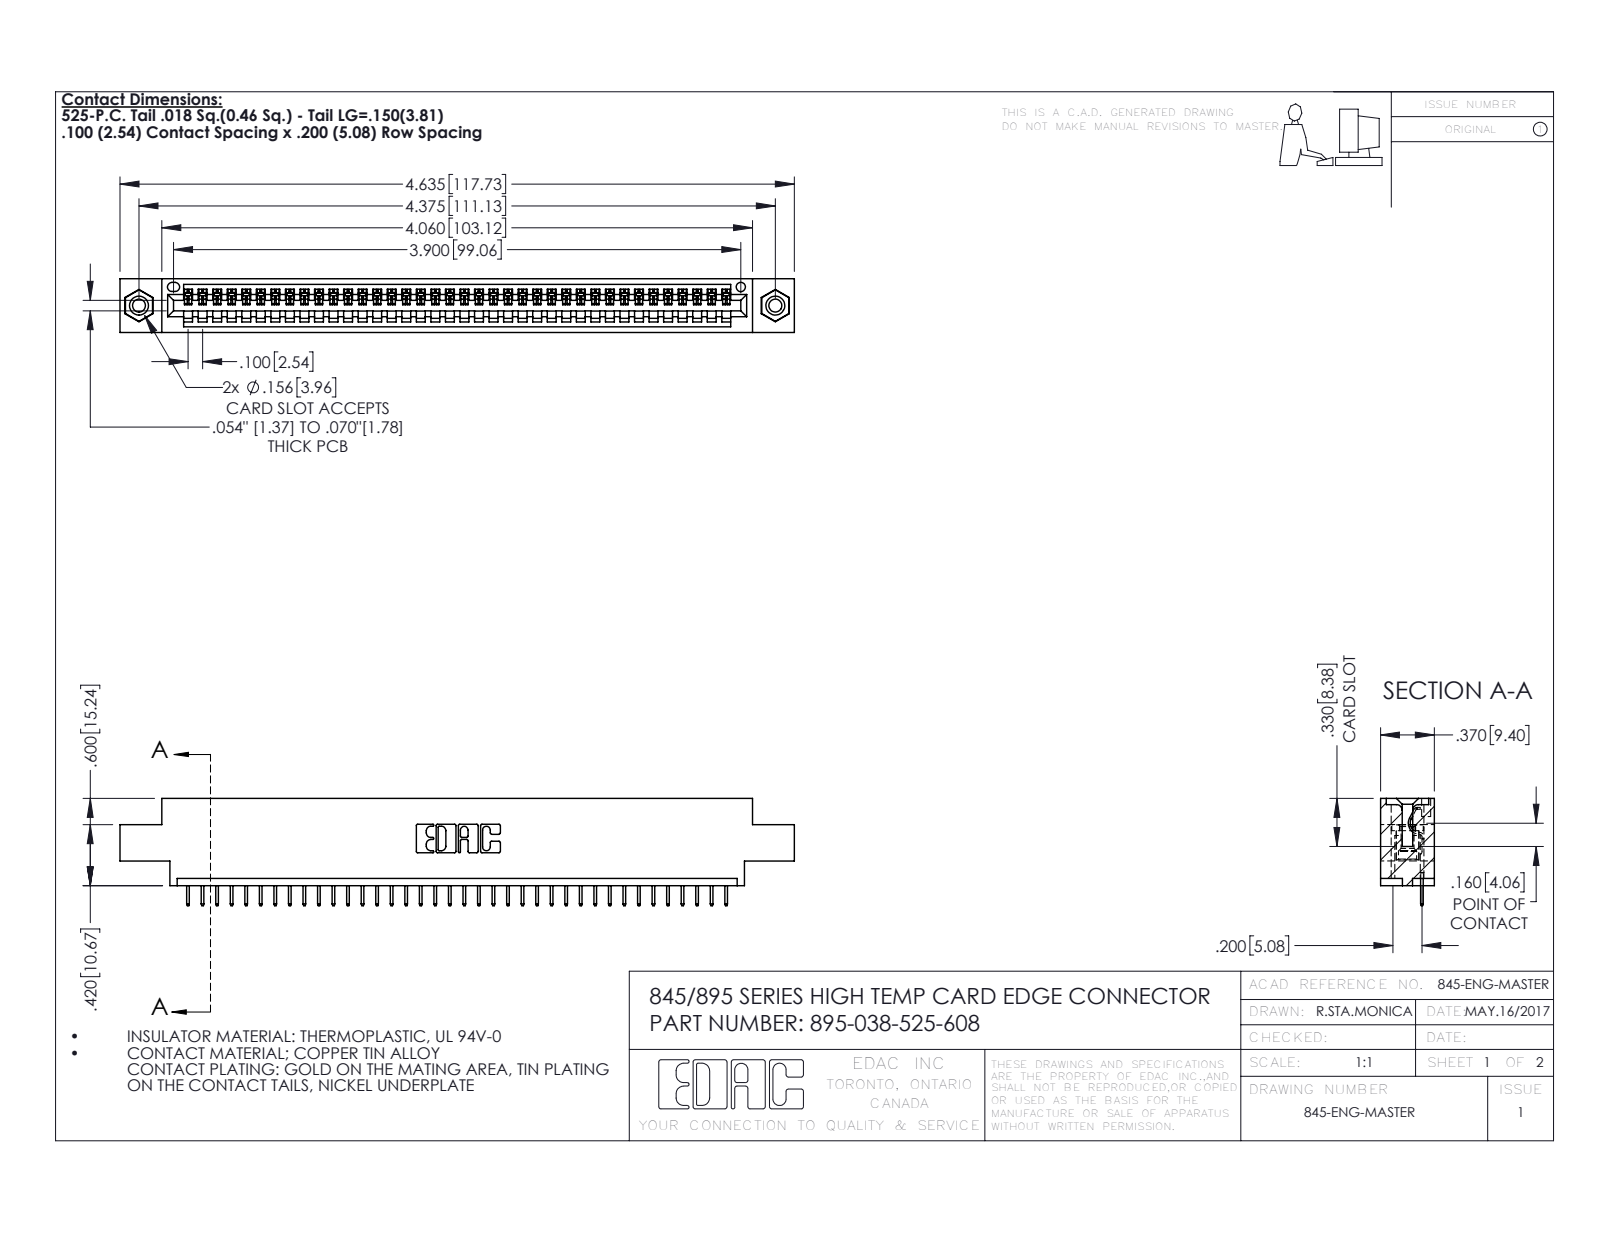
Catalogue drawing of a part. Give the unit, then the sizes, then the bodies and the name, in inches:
Units: inches
Overall size (bounding box): 4.635 × 0.737 × 0.37
Round holes (diameter × count): ⌀0.089 ×2, ⌀0.125 ×2, ⌀0.156 ×2, ⌀0.064 ×1
Round bosses / shafts (diameter × count): ⌀0.155 ×2
Partial cylindrical surfaces — rounded edges, fillets, slot ends (radius × count): R0.006 ×76, R0.01 ×22, R0.007 ×6, R0.031 ×6, R0.026 ×3, R0.031 ×2, R0.04 ×2, R0.014 ×1
Main face-to-face distances: 0.072, 0.298, 0.37, 0.2, 0.098, 0.272, 0.025, 0.225, 0.072, 0.175
Hole centre spacings: 0.27, 4.139, 4.375
Volume: 0.664 in³ · Surface area: 21.74 in²
Bodies: 41 solids, 2546 faces (1864 planar, 666 cylindrical, 16 other)
Part name (STEP PRODUCT): 895-038-525-608; 345-292-001_345-293-125; 845 Part_0.170 Offset - 0.156 Dia-TI; 345-250-001_345-250-003-102
STEP written by: SolidWorks 2020 (CONFIG_CONTROL_DESIGN)
